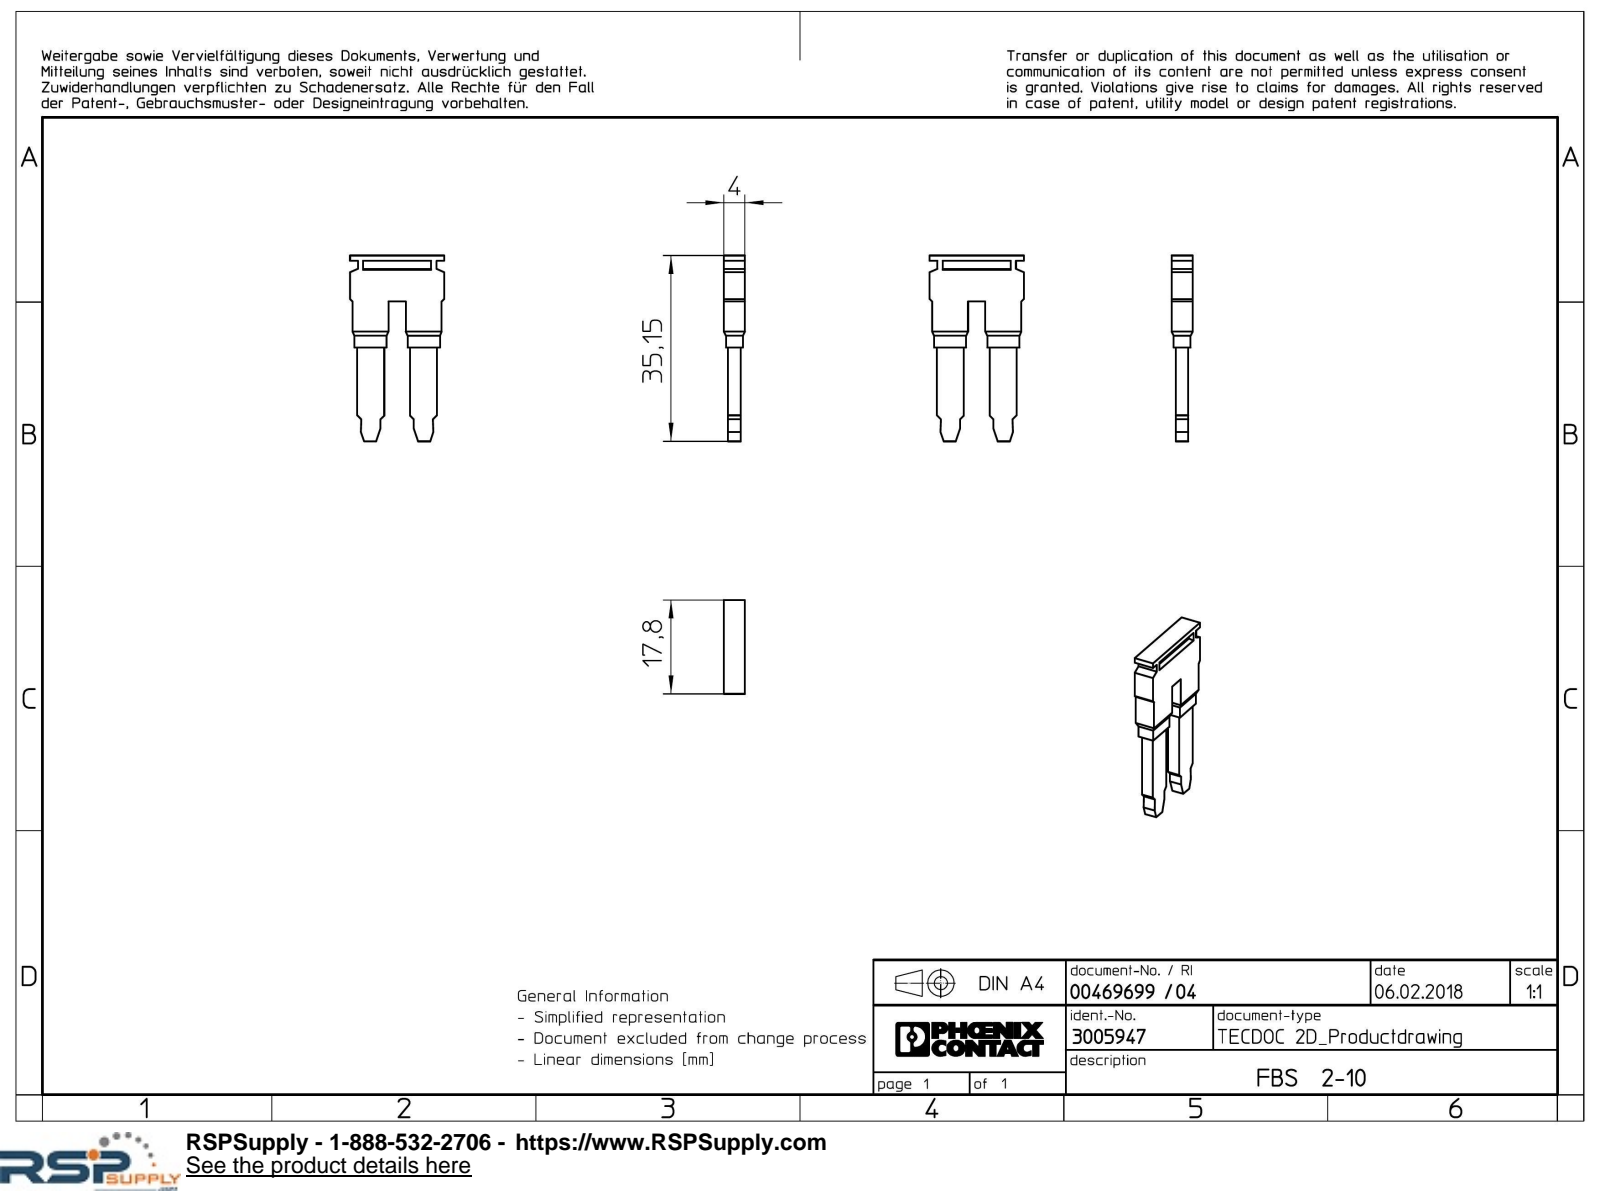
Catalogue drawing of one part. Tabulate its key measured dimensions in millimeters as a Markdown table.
| quantity | value |
| --- | --- |
| part name | FBS_2-10-select |
| STEP written by | Creo Elements/Direct Modeling 20.1A 29-Sep-2018 (C) Parametric Technology GmbH (AUTOMOTIVE_DESIGN) |
| units | millimeters |
| bodies | 1 solid, 70 faces (70 planar, 0 cylindrical, 0 other) |
| overall size | 35.15 × 17.8 × 4 |
| volume | 1 386 mm³ |
| surface area | 1 421 mm² |
| main face-to-face distances | 0.8, 3.2, 4, 2.4, 0.4, 1, 6.45, 5.1, 10, 10.55 |
